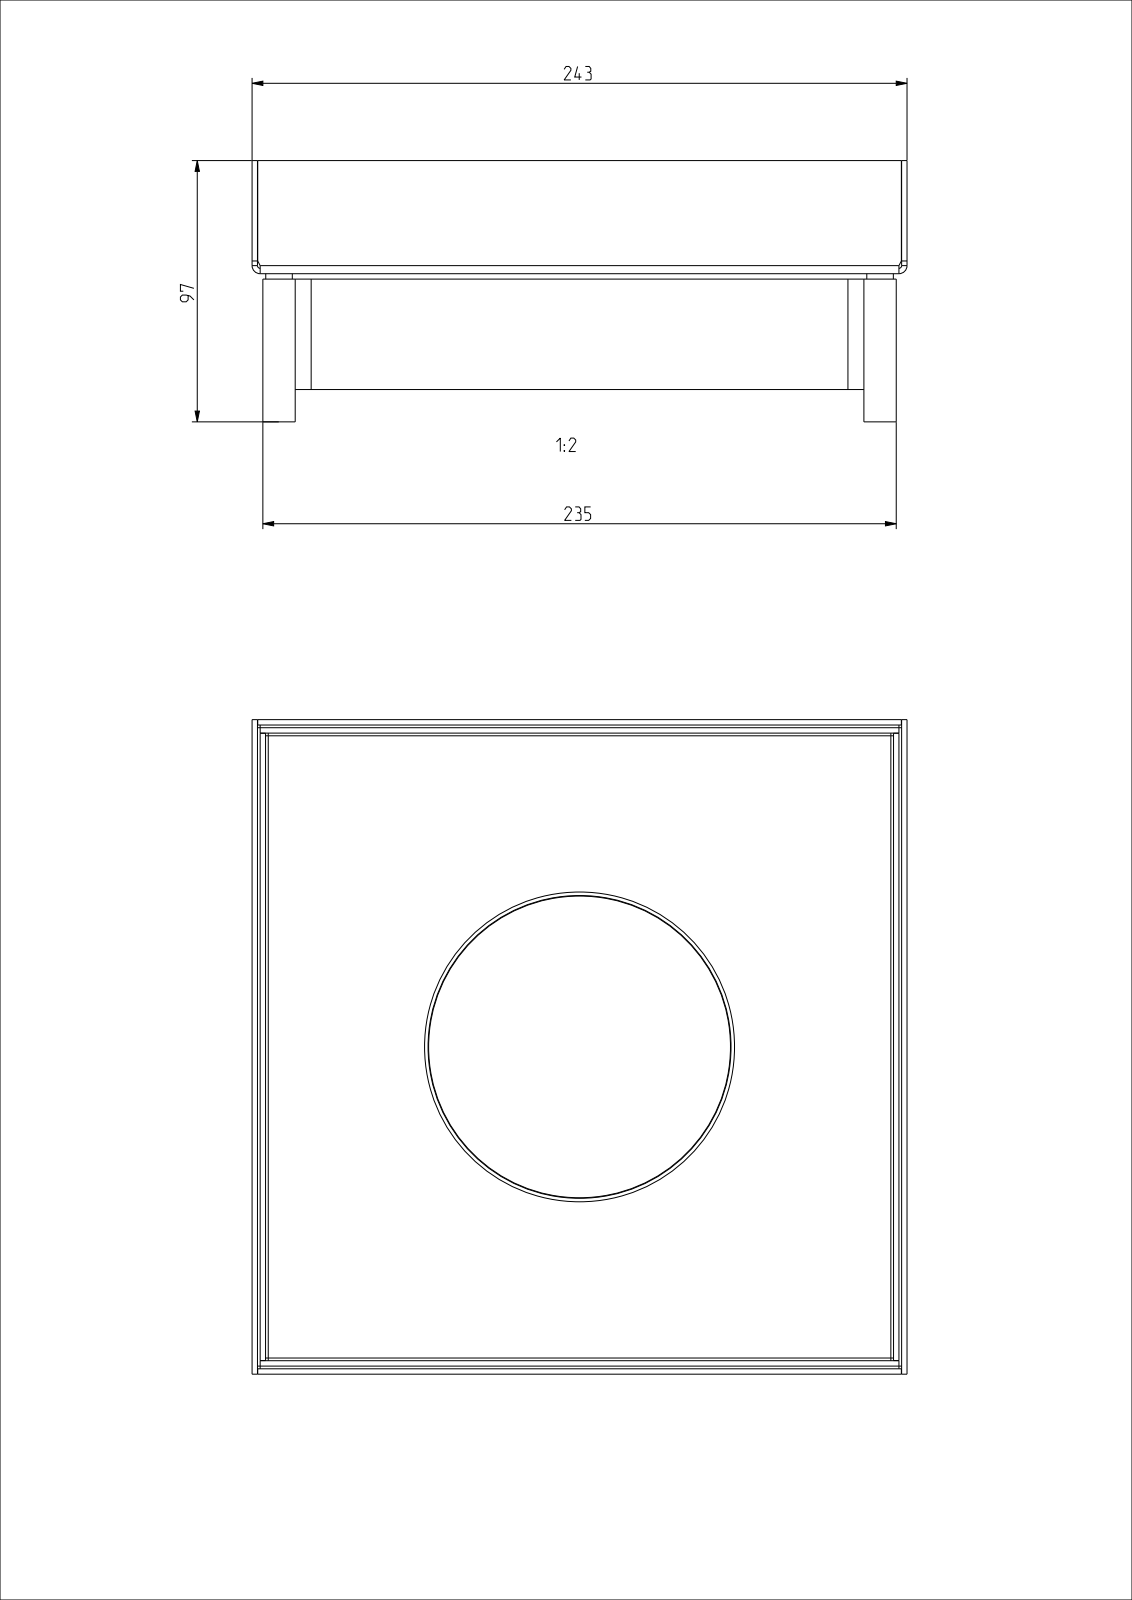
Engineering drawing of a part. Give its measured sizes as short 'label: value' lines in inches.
name: T-00631; T-00632; T-00625; T-00828_ASM (+8 more)
written by: CREO PARAMETRIC BY PTC INC, 2022024 (AUTOMOTIVE_DESIGN)
unit: in
bodies: 12 solids, 273 faces (148 planar, 115 cylindrical, 10 other)
size: 9.567 × 9.567 × 3.819
volume: 53.07 in³; area: 784.6 in²
holes: 4× ⌀0.197, 4× ⌀0.268, 4× ⌀0.335, 3× ⌀0.177, 1× ⌀3.173, 1× ⌀3.543, 1× ⌀3.976, 1× ⌀4.213, 1× ⌀4.276, 1× ⌀4.386, 1× ⌀4.409, 1× ⌀4.425
bosses: 4× ⌀0.472, 4× ⌀0.388, 1× ⌀4.528, 1× ⌀4.394, 1× ⌀4.37, 1× ⌀4.134, 1× ⌀3.843
rounds: 8× R0.039, 8× R0.118, 4× R0.079, 3× R0.197, 1× R1.693, 1× R5.906, 1× R6.004
face distances: 0.079, 0.118, 9.252, 0.098, 0.472, 0.394, 9.37, 0.197, 0.138, 9.232
hole spacings: 6.694, 2.506, 3.543, 3.703, 6.208, 8.713, 8.78, 2.126
